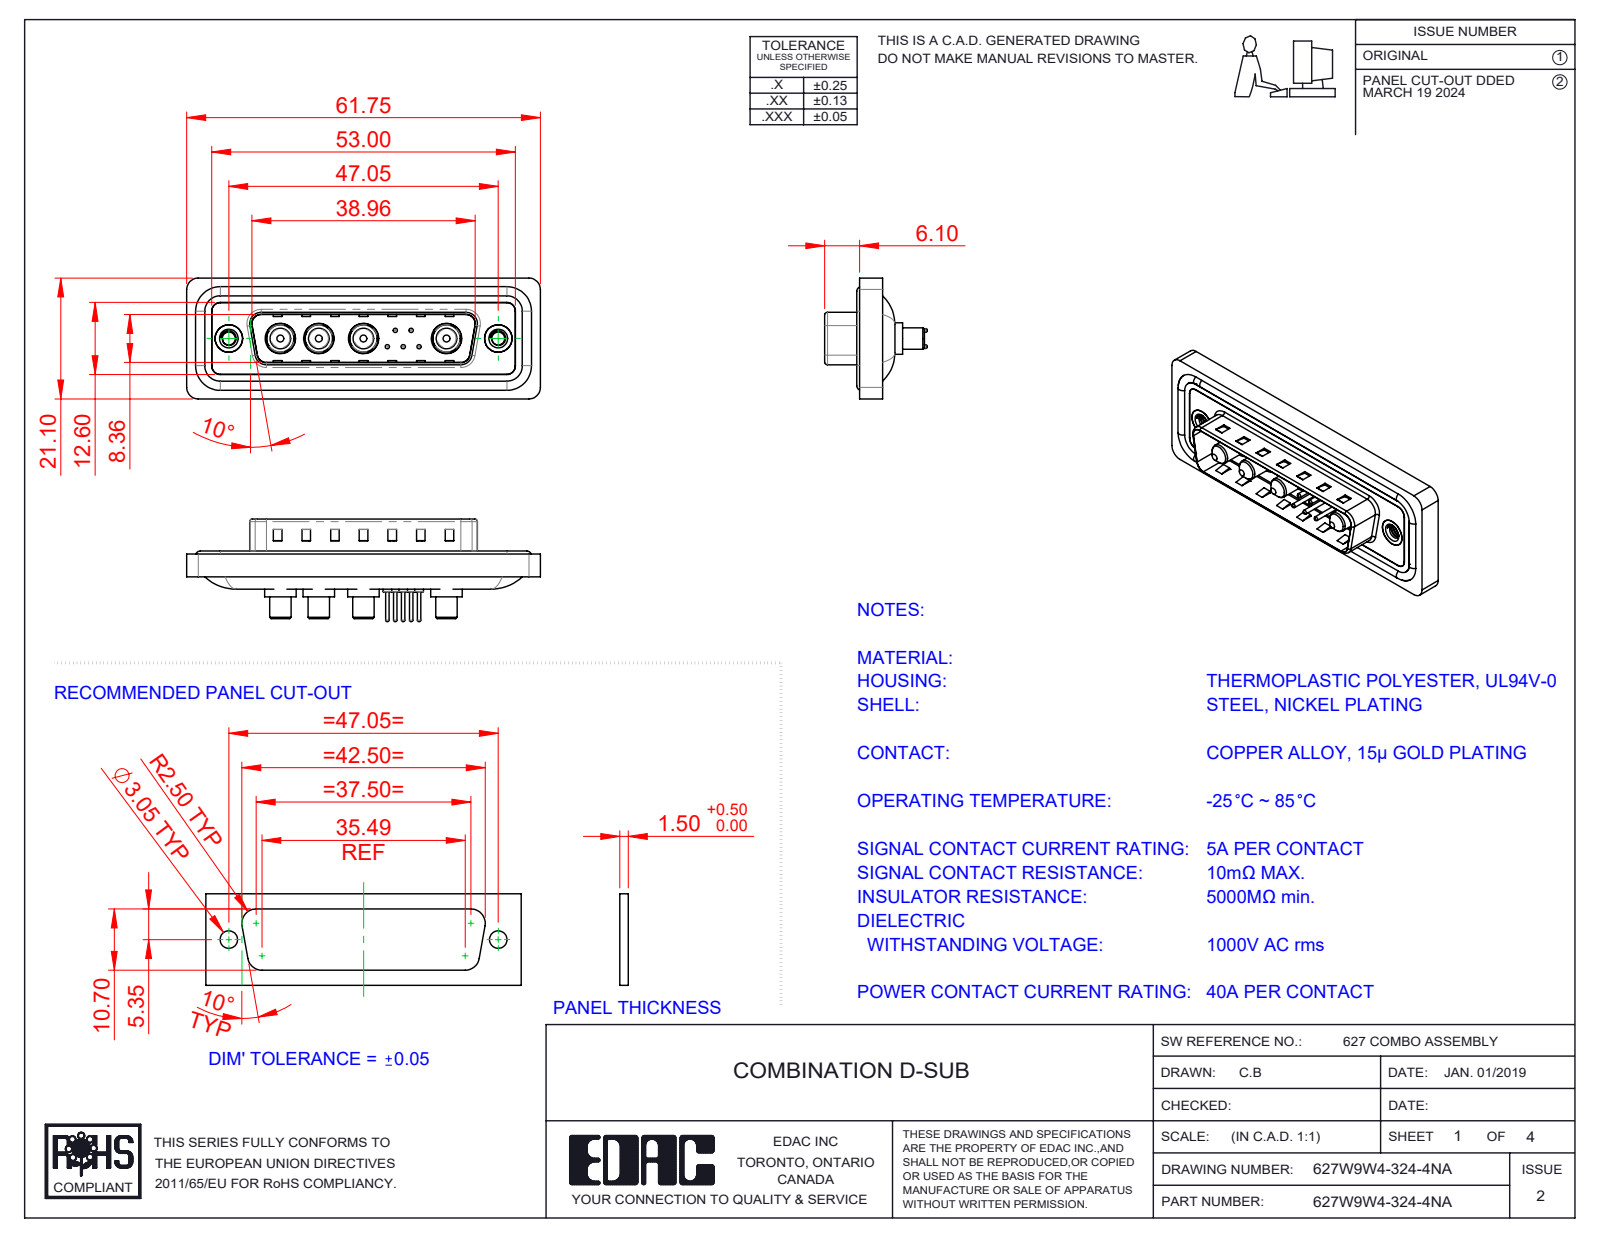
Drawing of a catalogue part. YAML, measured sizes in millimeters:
part_name: "627Combo Threaded Rivet_A; 627Combo Contact Row 2_24; 627Combo Shell Rear_25 Contacts; 627W9W4-324-4NA (+5 more)"
step_written_by: "SolidWorks 2023 (CONFIG_CONTROL_DESIGN)"
units: millimeters
bodies: {solids: 20, faces: 822, planar: 284, cylindrical: 336, other: 202}
overall_size: [61.75, 21.1, 17.9]
volume: 7480
surface_area: 11877
round_holes:
  - {diameter: 0.75, count: 5}
  - {diameter: 1.6, count: 5}
  - {diameter: 2, count: 5}
  - {diameter: 4.85, count: 4}
  - {diameter: 5.3, count: 4}
  - {diameter: 2.26, count: 2}
  - {diameter: 4, count: 2}
  - {diameter: 4.8, count: 2}
  - {diameter: 5, count: 2}
round_bosses_or_shafts:
  - {diameter: 1.5, count: 5}
  - {diameter: 0.6, count: 5}
  - {diameter: 5.5, count: 4}
  - {diameter: 5.2, count: 4}
  - {diameter: 4.75, count: 4}
  - {diameter: 3.75, count: 4}
  - {diameter: 3.6, count: 4}
  - {diameter: 1.6, count: 4}
partial_cylinders:
  - {radius: 1.5, count: 22}
  - {radius: 2, count: 18}
  - {radius: 0.5, count: 8}
  - {radius: 1.6, count: 8}
  - {radius: 0.25, count: 4}
  - {radius: 0.6, count: 4}
  - {radius: 0.65, count: 4}
  - {radius: 0.9, count: 4}
face_to_face_distances: [0.4, 1.5, 1.1, 0.5, 1.6, 3.1, 2.9, 0.82, 9.58, 5.65]
hole_center_spacings: [3.16, 2.77, 5.04, 14.51, 2.78, 4.4, 4.41, 5]
